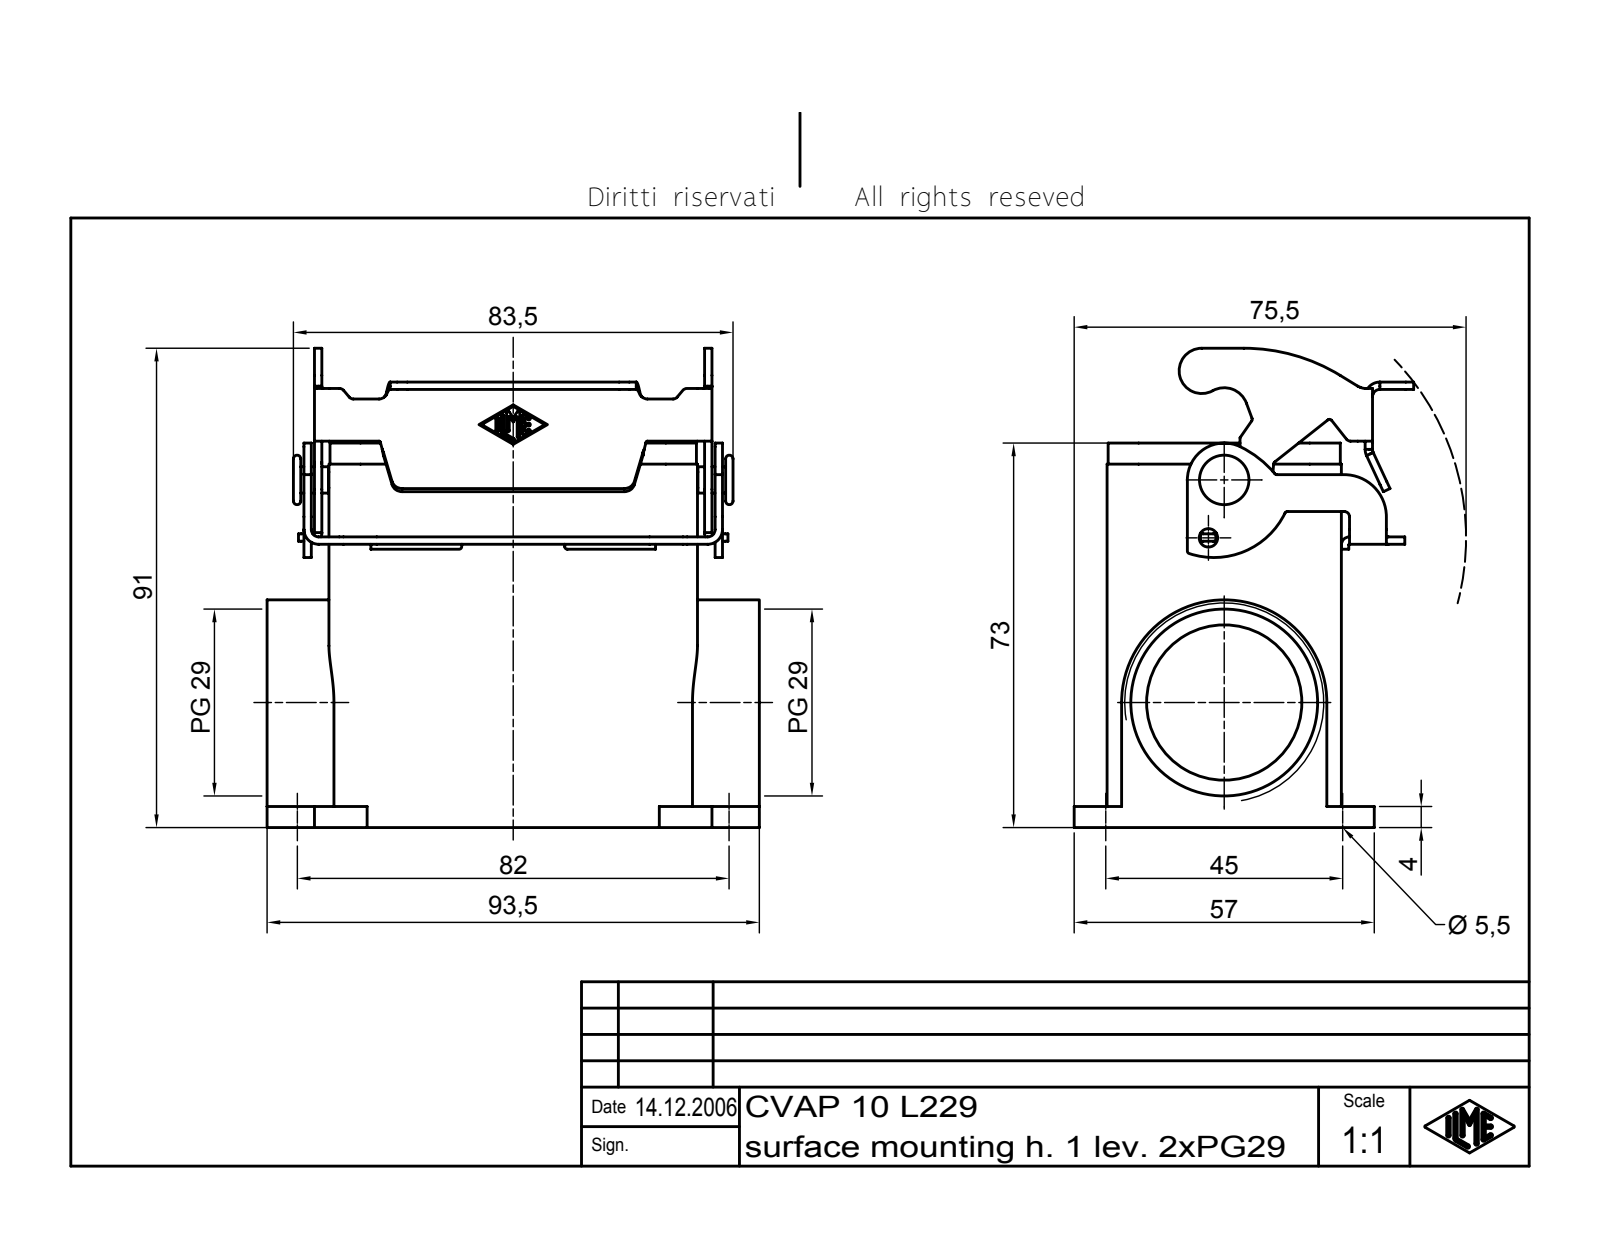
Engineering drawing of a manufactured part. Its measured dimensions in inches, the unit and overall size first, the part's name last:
Units: inches
Overall size (bounding box): 3.681 × 3.583 × 2.539
Round holes (diameter × count): ⌀0.217 ×4, ⌀0.138 ×1, ⌀1.161 ×1, ⌀1.397 ×1
Round bosses / shafts (diameter × count): ⌀0.197 ×1, ⌀0.126 ×1, ⌀0.118 ×1
Partial cylindrical surfaces — rounded edges, fillets, slot ends (radius × count): R0.01 ×15, R0.02 ×9, R0.059 ×9, R0.039 ×8, R0.055 ×6, R0.079 ×6, R0.11 ×6, R0.071 ×4
Main face-to-face distances: 0.157, 1.594, 1.752, 1.437, 0.055, 0.394, 2.362, 0.236, 0.463, 0.856
Hole centre spacings: 1.772, 3.228, 3.683, 1.236
Volume: 5.935 in³ · Surface area: 80.63 in²
Bodies: 2 solids, 403 faces (141 planar, 118 cylindrical, 144 other)
Part name (STEP PRODUCT): CVAP 10 L229
STEP written by: Autodesk Inventor 7 (AUTOMOTIVE_DESIGN)
